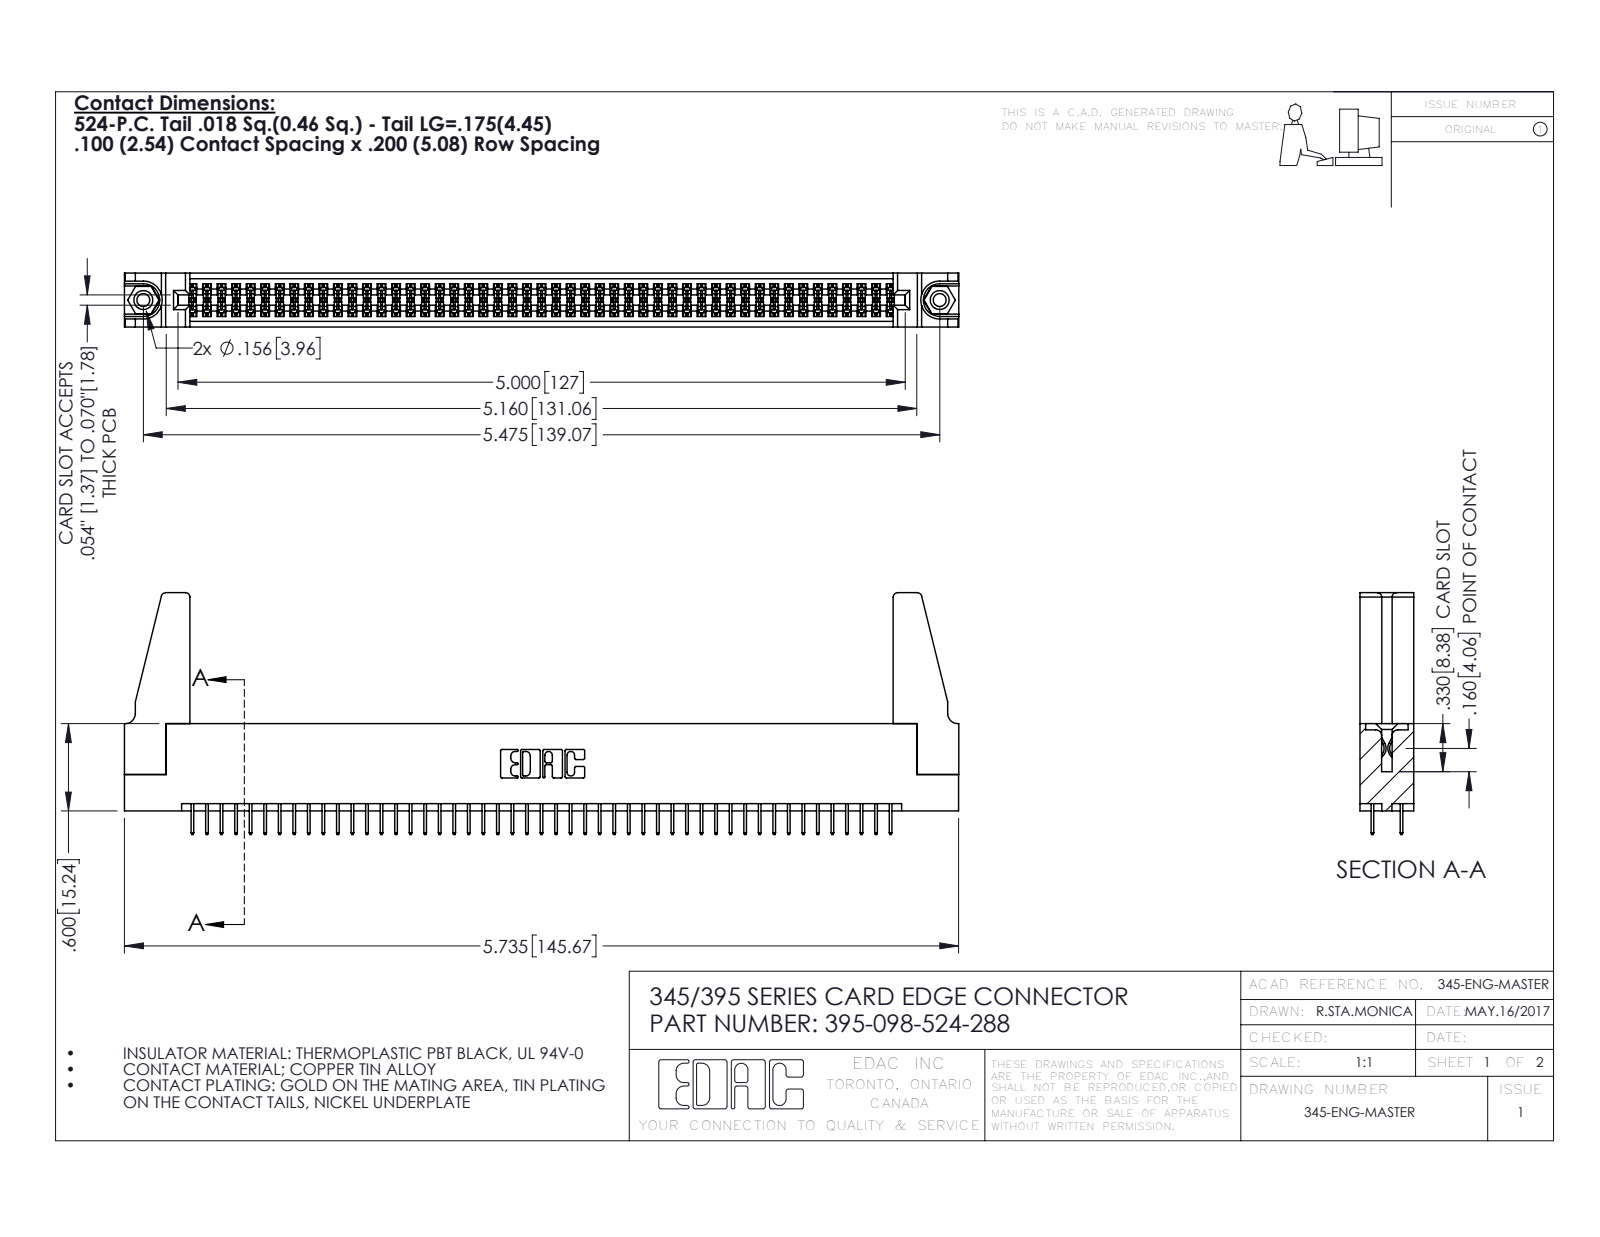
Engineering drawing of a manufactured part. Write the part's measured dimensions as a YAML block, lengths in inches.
part_name: "345-292-001_345-293-124; 345 Part_Flush Mounting Lugs - 0.156 Dia-TH; 345-250-001_345-250-001-102; 395-098-524-288 (+1 more)"
step_written_by: "SolidWorks 2016 (CONFIG_CONTROL_DESIGN)"
units: inches
bodies: {solids: 103, faces: 5542, planar: 3974, cylindrical: 1552, other: 16}
overall_size: [5.736, 1.662, 0.37]
volume: 1.057
surface_area: 36.68
round_holes:
  - {diameter: 0.089, count: 2}
  - {diameter: 0.125, count: 2}
  - {diameter: 0.156, count: 2}
  - {diameter: 0.064, count: 1}
round_bosses_or_shafts:
  - {diameter: 0.155, count: 2}
partial_cylinders:
  - {radius: 0.006, count: 147}
  - {radius: 0.01, count: 22}
  - {radius: 0.03, count: 8}
  - {radius: 0.007, count: 6}
  - {radius: 0.031, count: 6}
  - {radius: 0.026, count: 3}
  - {radius: 0.014, count: 2}
  - {radius: 0.019, count: 2}
face_to_face_distances: [0.072, 0.298, 0.37, 0.2, 0.098, 0.272, 0.025, 0.225, 0.072, 0.175]
hole_center_spacings: [0.27, 5.239, 5.475]
